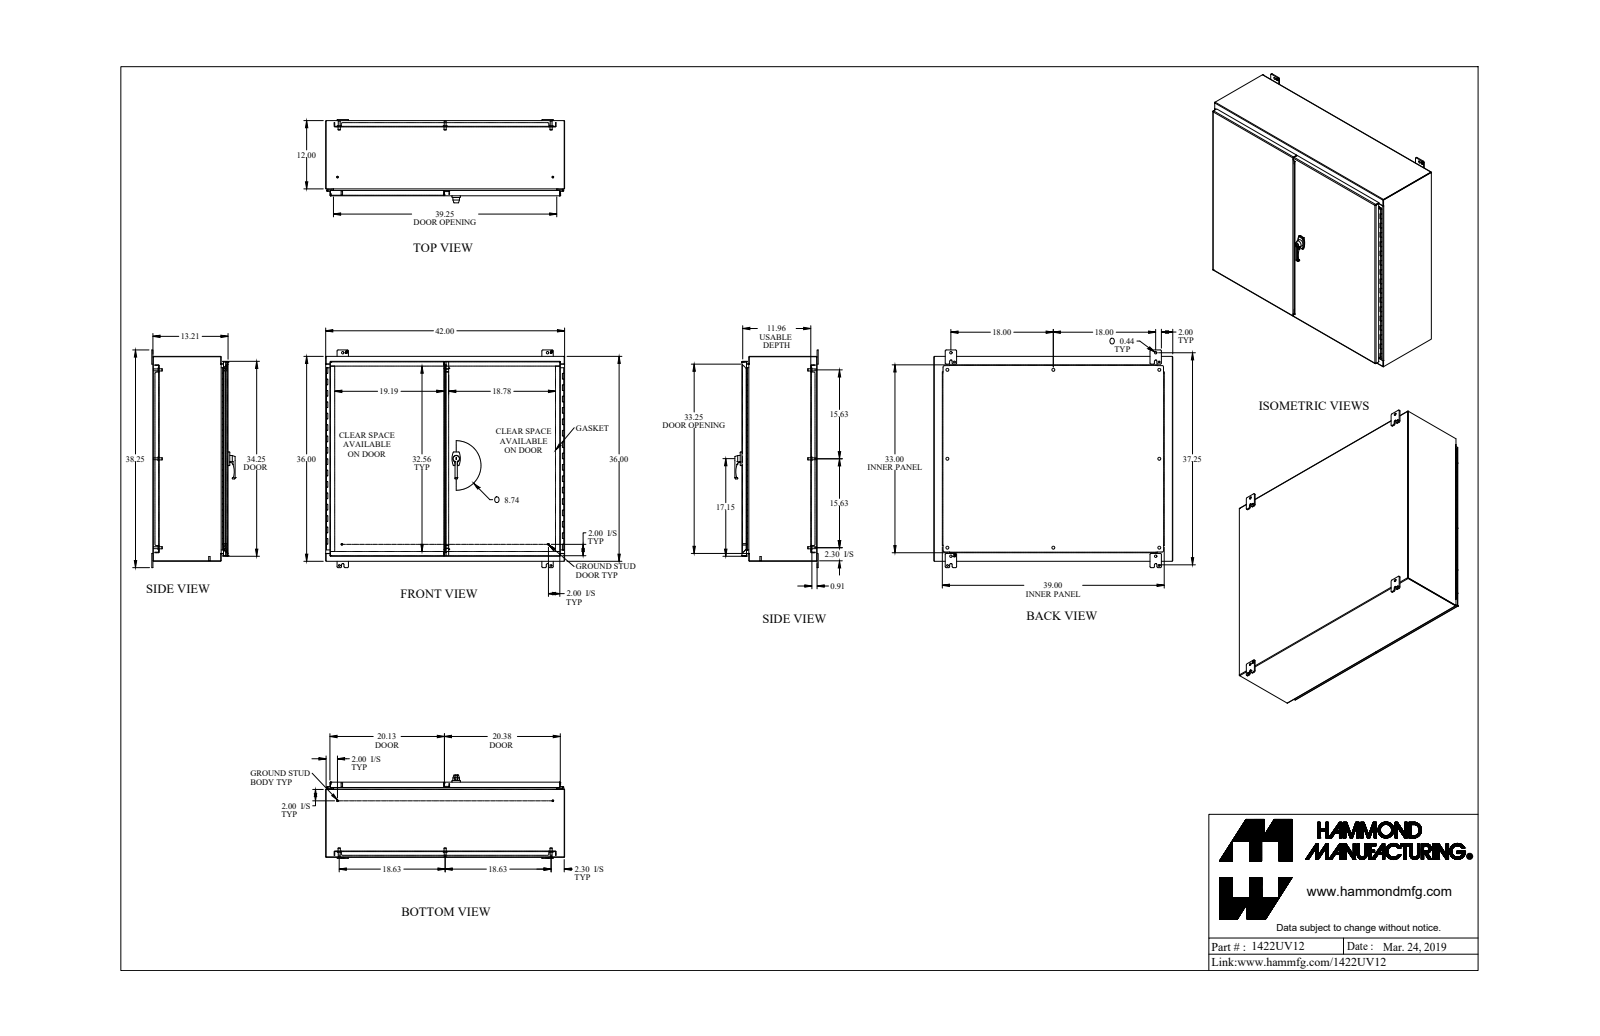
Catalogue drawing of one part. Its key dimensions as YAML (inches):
part_name: "1422UV12"
step_written_by: "SolidWorks 2019 (AUTOMOTIVE_DESIGN)"
units: inches
bodies: {solids: 0, faces: 1731, planar: 1092, cylindrical: 521, other: 118}
overall_size: [42, 38.25, 14.637]
round_holes:
  - {diameter: 0.304, count: 12}
  - {diameter: 0.307, count: 9}
  - {diameter: 0.445, count: 9}
  - {diameter: 0.5, count: 8}
  - {diameter: 0.218, count: 4}
  - {diameter: 0.313, count: 4}
  - {diameter: 0.437, count: 4}
  - {diameter: 0.215, count: 3}
  - {diameter: 0.11, count: 2}
  - {diameter: 0.127, count: 2}
  - {diameter: 0.156, count: 2}
  - {diameter: 0.187, count: 2}
round_bosses_or_shafts:
  - {diameter: 1, count: 10}
  - {diameter: 0.65, count: 8}
  - {diameter: 0.375, count: 8}
  - {diameter: 0.33, count: 8}
  - {diameter: 0.5, count: 5}
  - {diameter: 0.313, count: 4}
  - {diameter: 0.281, count: 4}
  - {diameter: 0.25, count: 4}
partial_cylinders:
  - {radius: 0.188, count: 27}
  - {radius: 0.048, count: 18}
  - {radius: 0.143, count: 18}
  - {radius: 0.05, count: 16}
  - {radius: 0.036, count: 14}
  - {radius: 0.108, count: 14}
  - {radius: 0.25, count: 13}
  - {radius: 0.116, count: 12}
face_to_face_distances: [0.072, 0.095, 13.043, 13.115, 0.095, 0.937, 13.138, 13.21, 12.106, 12.011]
hole_center_spacings: [6, 40.835, 12, 42.137, 18, 40.392, 44.221, 3.387]
